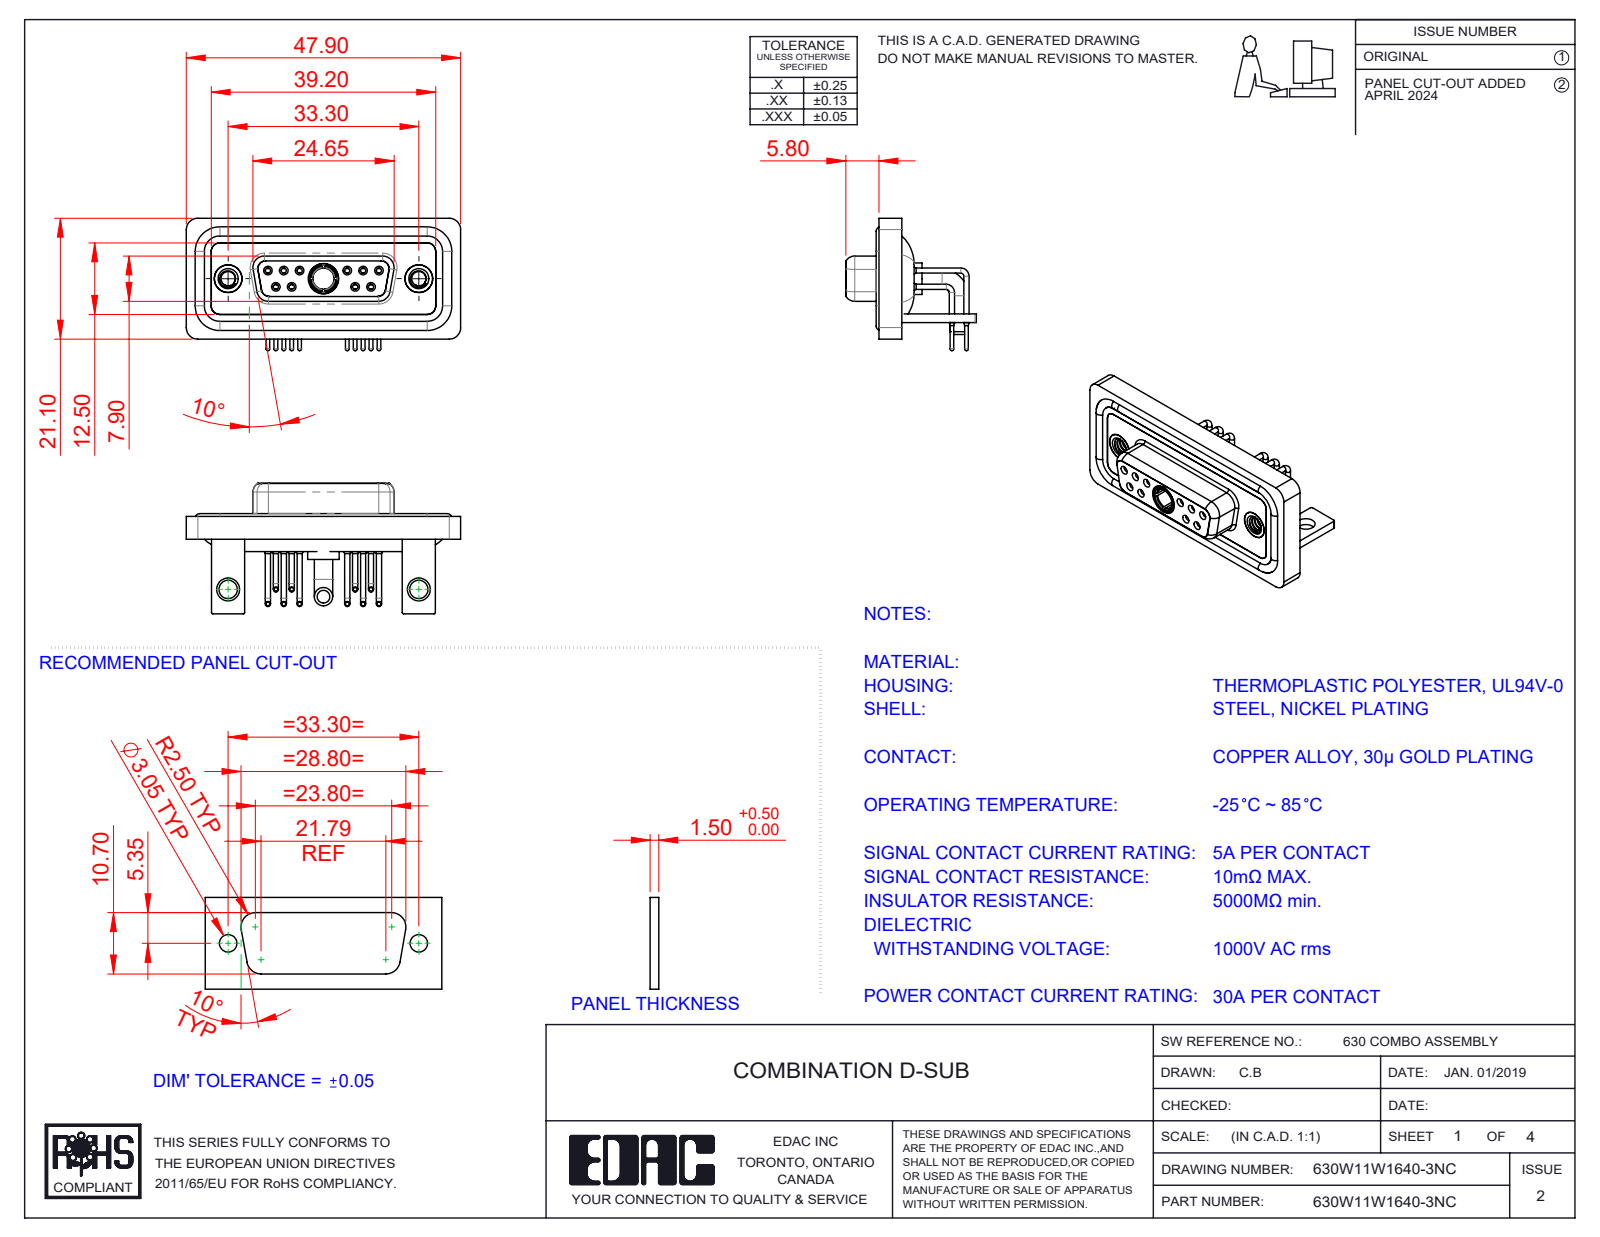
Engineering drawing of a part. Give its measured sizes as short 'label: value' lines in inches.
name: 630Combo Housing_11W1; Power Socket_30A RA; 630Combo Contact Row 2_50 Contacts; 630Combo Contact Row 1_50 Contacts (+6 more)
written by: SolidWorks 2023 (CONFIG_CONTROL_DESIGN)
unit: in
bodies: 21 solids, 1036 faces (304 planar, 465 cylindrical, 267 other)
size: 1.886 × 0.91 × 0.898
volume: 0.403 in³; area: 17.4 in²
holes: 10× ⌀0.035, 10× ⌀0.043, 10× ⌀0.059, 10× ⌀0.079, 6× ⌀0.067, 4× ⌀0.063, 3× ⌀0.191, 2× ⌀0.098, 2× ⌀0.126, 2× ⌀0.157, 2× ⌀0.159, 2× ⌀0.197
bosses: 10× ⌀0.063, 10× ⌀0.035, 10× ⌀0.026, 2× ⌀0.195, 2× ⌀0.189, 2× ⌀0.126, 1× ⌀0.217, 1× ⌀0.205
rounds: 21× R0.079, 18× R0.059, 16× R0.01, 12× R0.053, 8× R0.063, 5× R0.02, 4× R0.024, 4× R0.026
face distances: 0.016, 0.114, 0.071, 0.059, 0.146, 0.043, 0.063, 0.161, 0.031, 0.098
hole spacings: 0.124, 0.109, 0.545, 0.436, 0.654, 0.198, 0.198, 0.218
